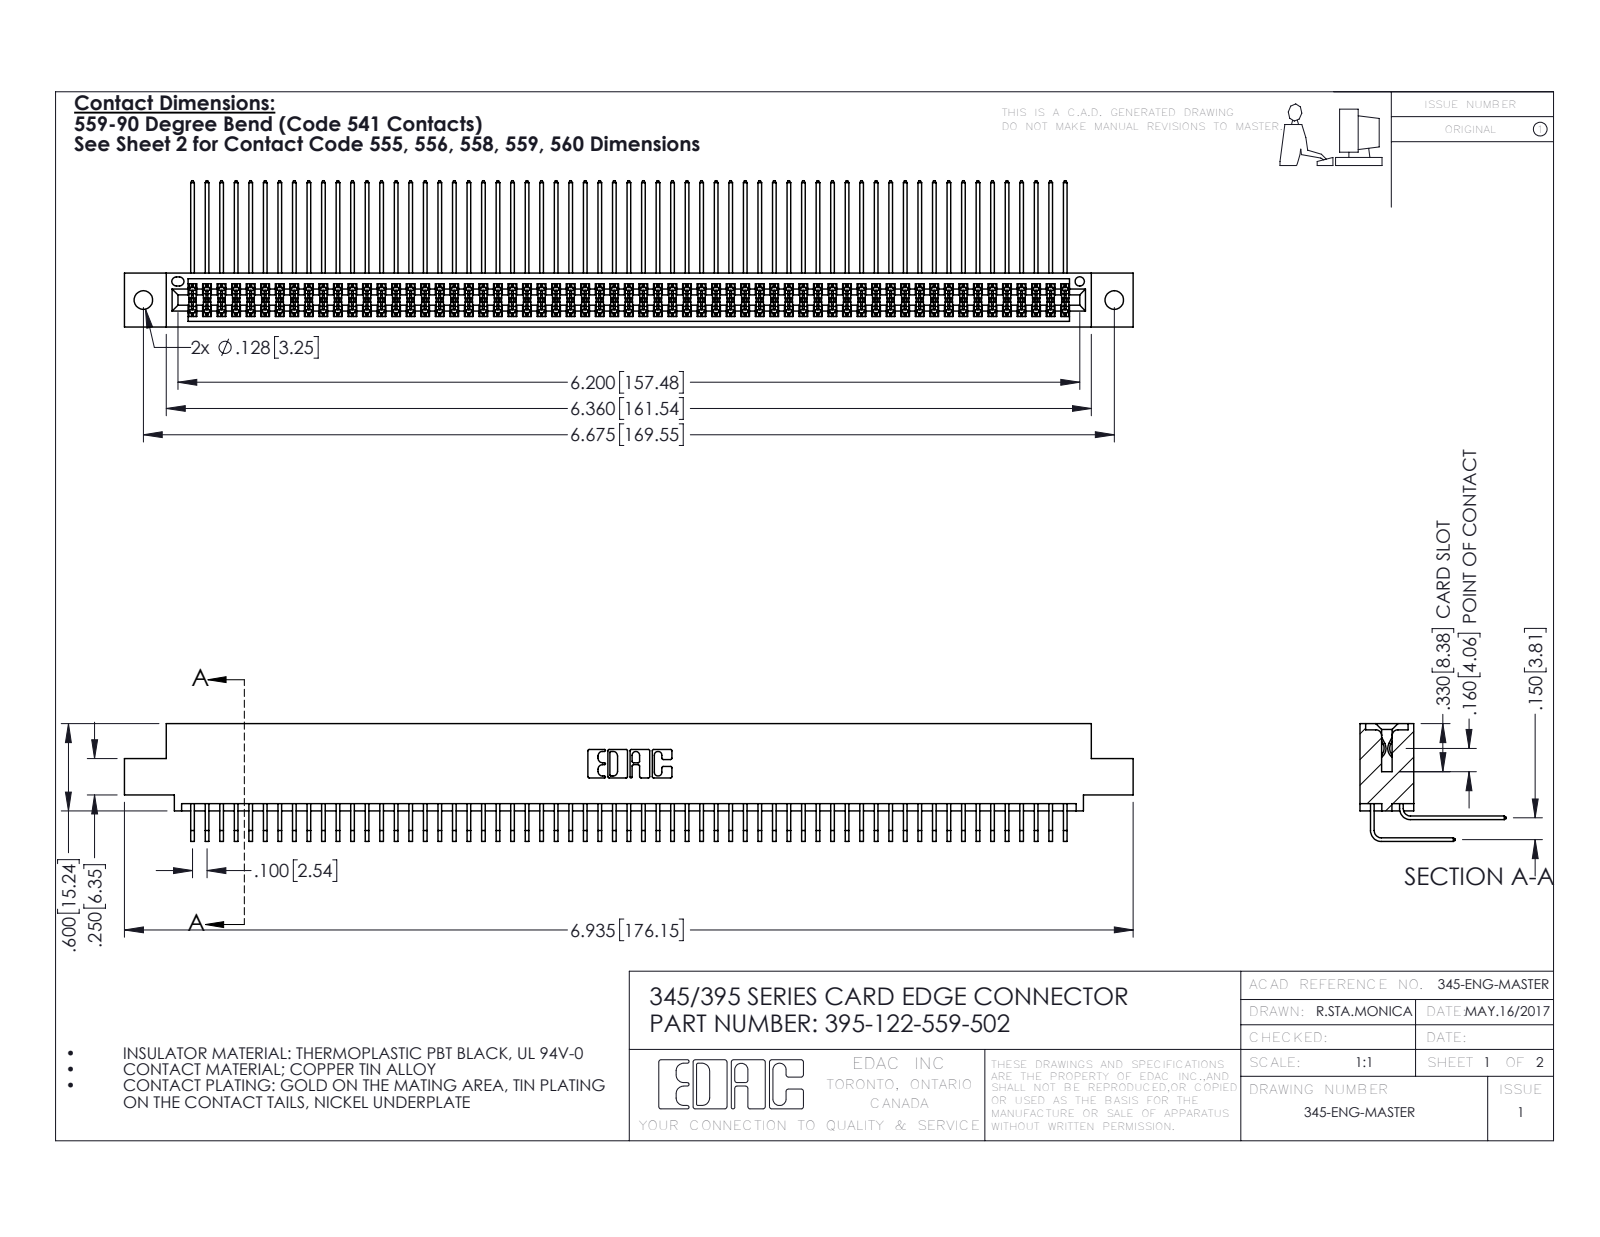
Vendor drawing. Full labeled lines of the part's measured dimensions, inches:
Part name (STEP PRODUCT): 345 Part_0.110 Offset - 0.128 Dia; 345-292-001_558 559 Tail - 1; 345-292-001_559 Tail - 2; 395-122-559-502
STEP written by: SolidWorks 2016 (CONFIG_CONTROL_DESIGN)
Units: inches
Bodies: 123 solids, 6474 faces (4354 planar, 2120 cylindrical, 0 other)
Overall size (bounding box): 6.935 × 1.005 × 0.809
Volume: 1.091 in³ · Surface area: 46.39 in²
Round holes (diameter × count): ⌀0.128 ×2, ⌀0.064 ×1
Partial cylindrical surfaces — rounded edges, fillets, slot ends (radius × count): R0.006 ×183, R0.01 ×22, R0.007 ×6, R0.031 ×6, R0.026 ×3, R0.014 ×2, R0.019 ×2, R0.022 ×2
Main face-to-face distances: 0.072, 0.298, 0.2, 0.37, 0.098, 0.272, 0.025, 0.225, 0.175, 0.15
Hole centre spacings: 0.27, 6.439, 6.675
